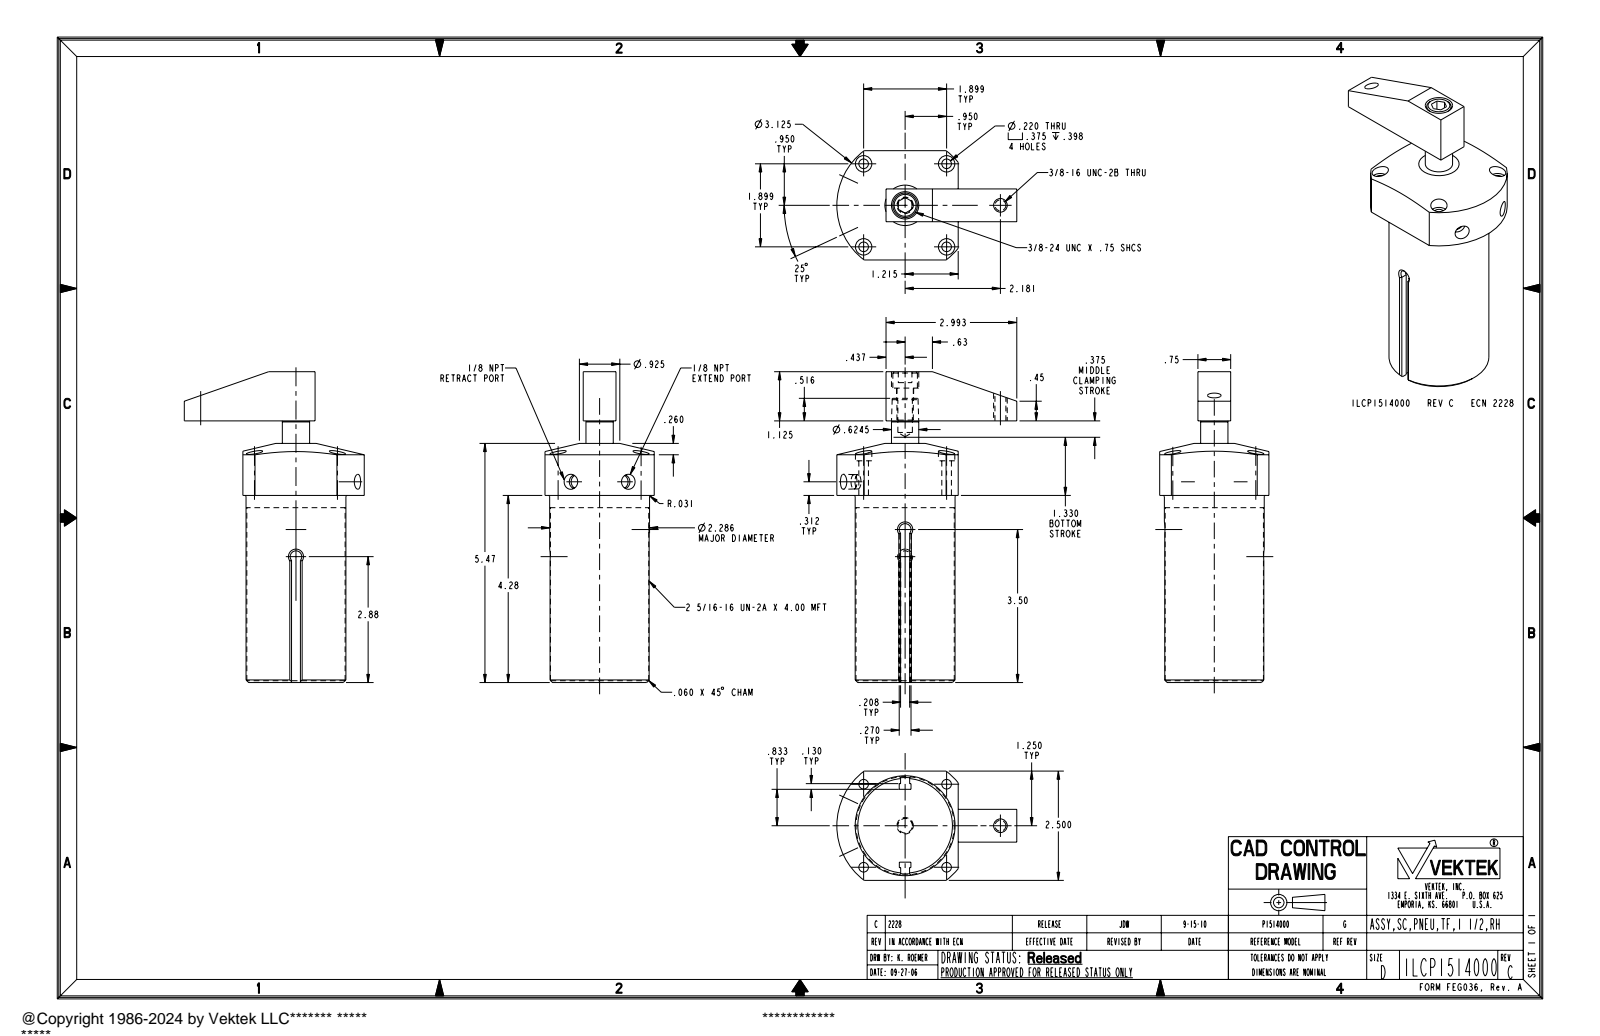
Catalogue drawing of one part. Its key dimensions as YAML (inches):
part_name: "ILCP1514000; ILC91501503; ILCP1514000_ASM"
step_written_by: "PRO/ENGINEER BY PARAMETRIC TECHNOLOGY CORPORATION, 2007460 (AUTOMOTIVE_DESIGN_CC2)"
units: inches
bodies: {solids: 2, faces: 123, planar: 52, cylindrical: 47, other: 24}
overall_size: [7.11, 4.119, 2.5]
volume: 25.67
surface_area: 107.2
round_holes:
  - {diameter: 0.22, count: 4}
  - {diameter: 0.375, count: 4}
  - {diameter: 0.328, count: 2}
  - {diameter: 0.312, count: 1}
  - {diameter: 0.332, count: 1}
  - {diameter: 0.39, count: 1}
  - {diameter: 0.625, count: 1}
round_bosses_or_shafts:
  - {diameter: 2.286, count: 1}
  - {diameter: 2.25, count: 1}
  - {diameter: 0.624, count: 1}
  - {diameter: 0.562, count: 1}
  - {diameter: 0.375, count: 1}
  - {diameter: 0.25, count: 1}
partial_cylinders:
  - {radius: 0.132, count: 1}
  - {radius: 0.135, count: 1}
  - {radius: 1.563, count: 1}
face_to_face_distances: [0.875, 1.625, 0.75, 4.28, 1.705, 5.985, 2.5, 0.417, 2.083, 0.458]
hole_center_spacings: [1.343, 1.899, 1.555, 2.686, 3.272, 2.181]
